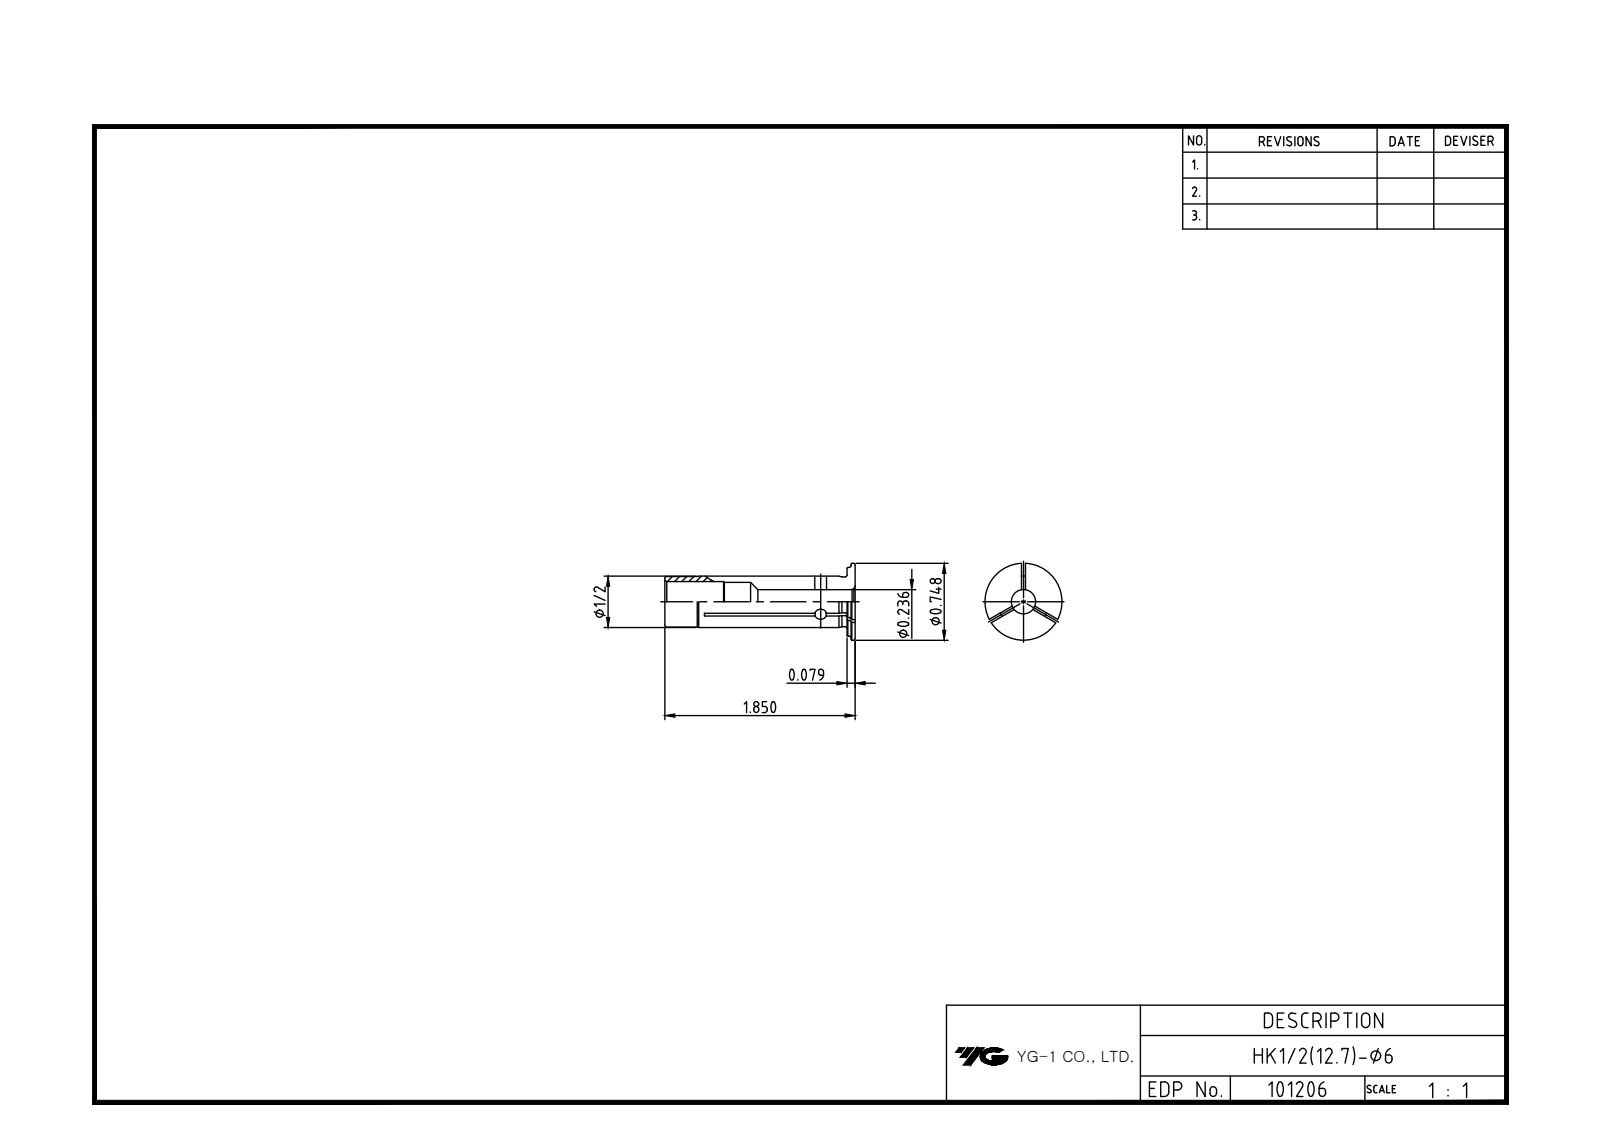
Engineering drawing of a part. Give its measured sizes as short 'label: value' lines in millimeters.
name: LO-HK12.7-6
written by: Autodesk Inventor 2025 (AP242_MANAGED_MODEL_BASED_3D_ENGINEERING_MIM_LF)
unit: mm
bodies: 1 solid, 12 faces (4 planar, 6 cylindrical, 2 other)
size: 47 × 19 × 19
volume: 3 820 mm³; area: 3 544 mm²
holes: 1× ⌀6, 1× ⌀9.6, 1× ⌀10
bosses: 1× ⌀19, 1× ⌀17, 1× ⌀12.7
face distances: 1, 2, 45, 46, 47
